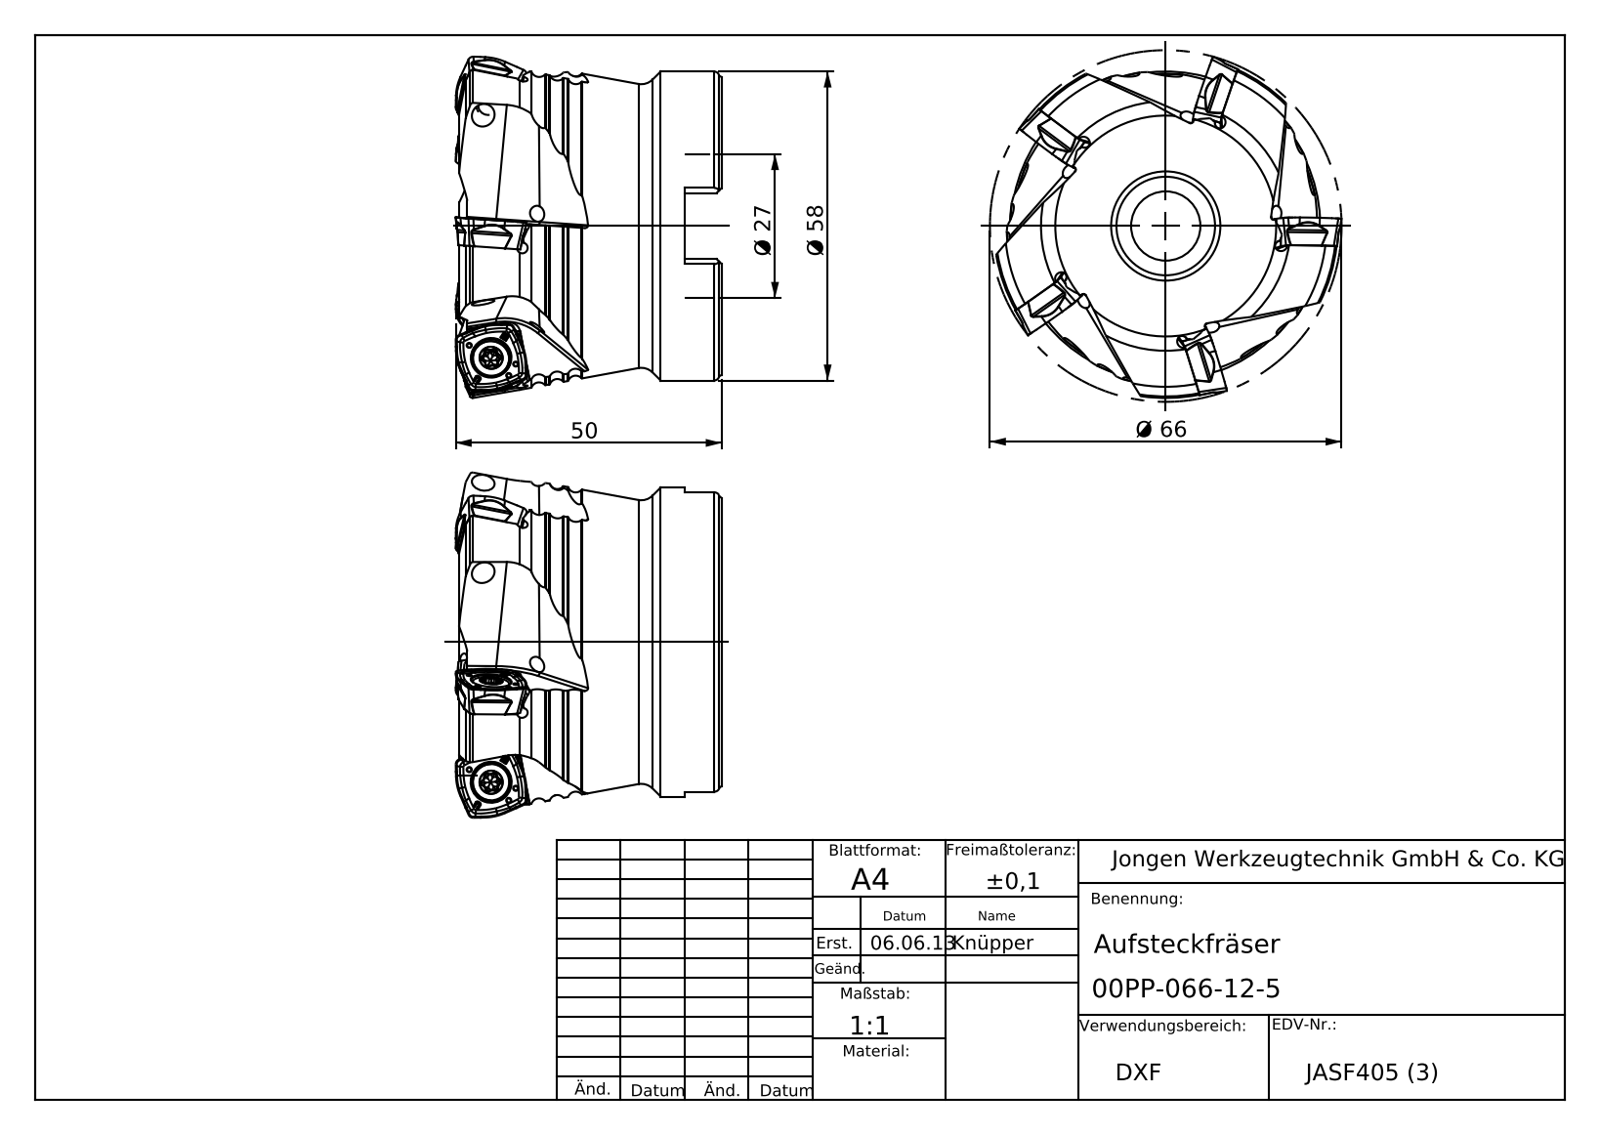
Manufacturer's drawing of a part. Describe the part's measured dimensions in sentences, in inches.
The part is named "JASF405 pk". Its 3-D file was written by "SolidWorks 2013 (AUTOMOTIVE_DESIGN)". It is 1 solid with 289 faces: 99 planar, 55 cylindrical and 135 other. Overall it measures 2.597 by 2.597 by 1.965 inches. Its volume is 6.516 cubic inches and its surface area 31.96 square inches. Round holes: 5 of diameter 0.118, 1 of diameter 0.512, 1 of diameter 0.728, 1 of diameter 1.063, 1 of diameter 1.069, 1 of diameter 1.075. Round bosses or shafts: 1 of diameter 2.283. Partial cylindrical surfaces (rounded edges, fillets, slot ends): 10 of radius 0.02, 10 of radius 0.051, 5 of radius 0.039, 5 of radius 0.079. The main face-to-face distances are 1.88, 0.276, 1.604, 0.866, 0.591, 1.014, 0.488, 1.37, 1.094, 0.504.
